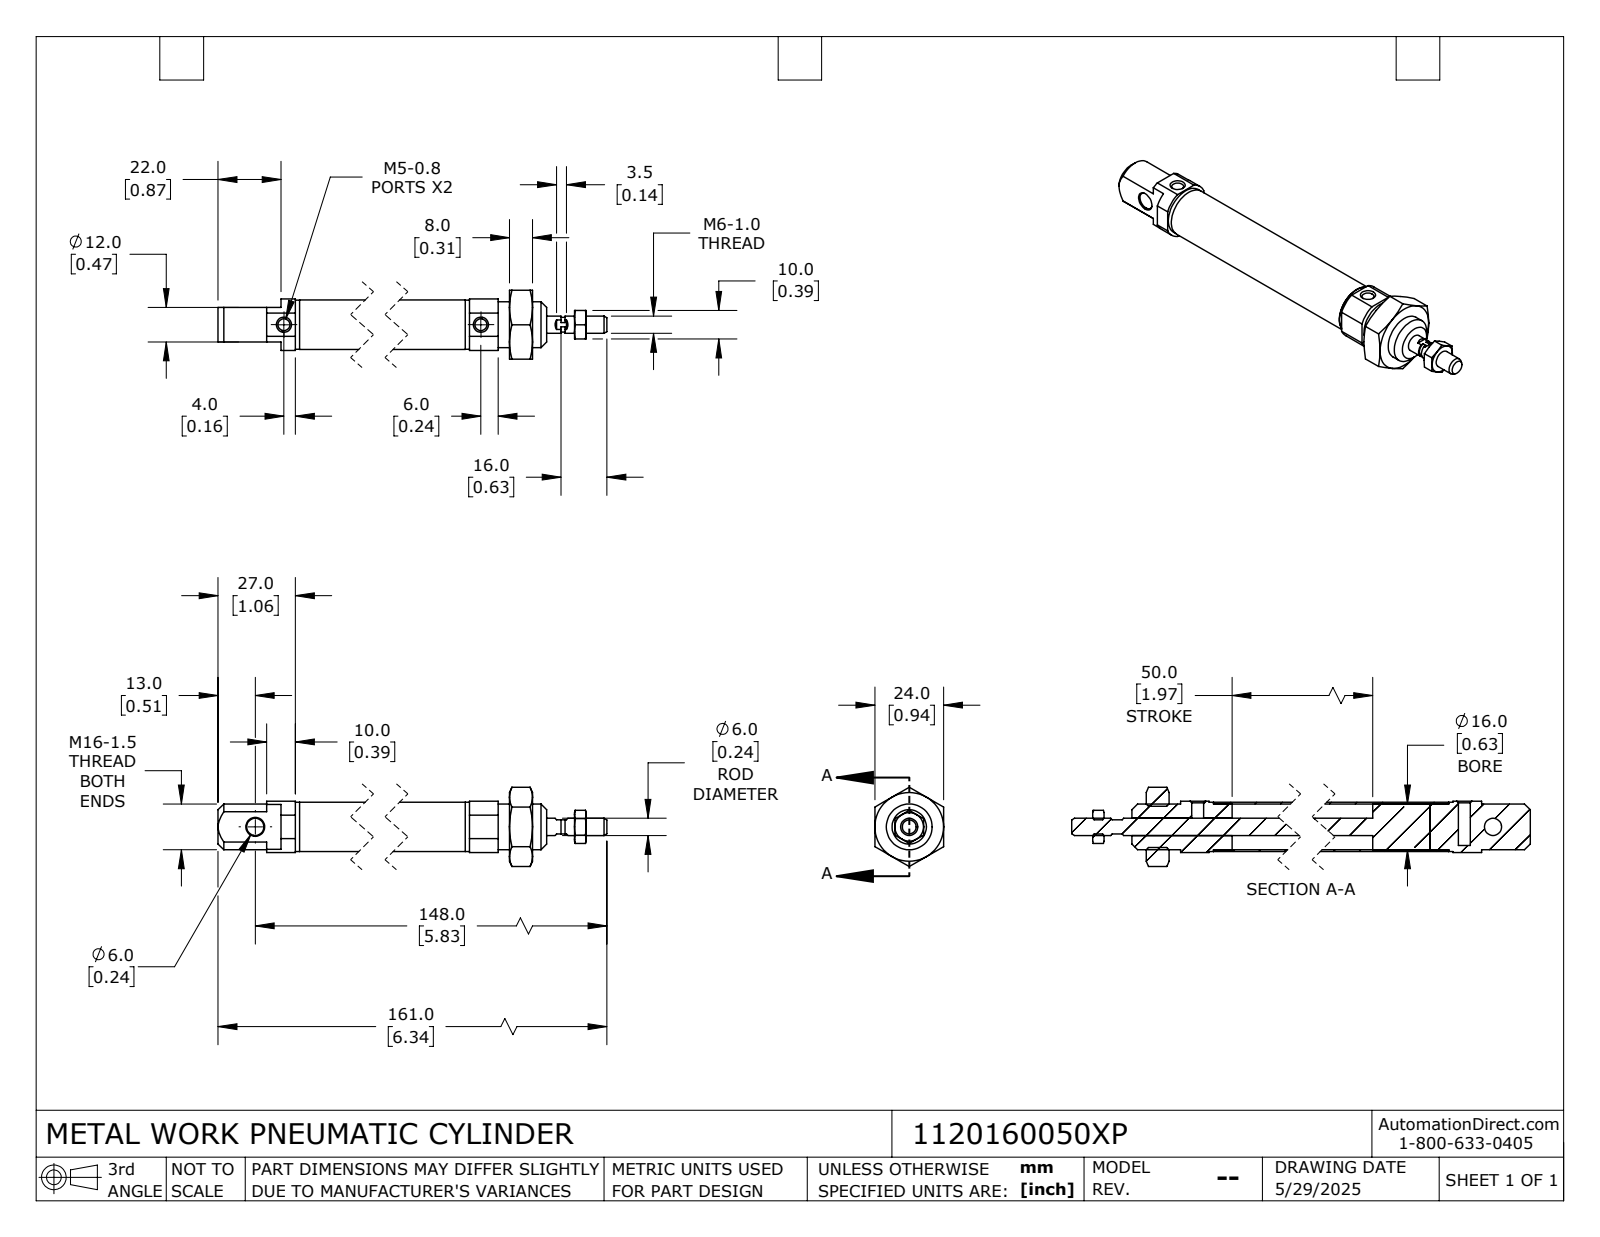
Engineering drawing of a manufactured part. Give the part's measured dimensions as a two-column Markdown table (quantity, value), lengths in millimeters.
| quantity | value |
| --- | --- |
| part name | 1120160050XP_BODY; 1120160050XP_ROD; 1120160050XP |
| STEP written by | SolidWorks 2024 (CONFIG_CONTROL_DESIGN) |
| units | millimeters |
| bodies | 6 solids, 146 faces (55 planar, 45 cylindrical, 46 other) |
| overall size | 161 × 27.71 × 24 |
| volume | 25 924 mm³ |
| surface area | 19 830 mm² |
| round holes (diameter × count) | 4.13 × 2, 4.92 × 1, 6 × 1, 14.38 × 1 |
| round bosses / shafts (diameter × count) | 17.27 × 1, 17.2 × 1, 16.15 × 1, 16 × 1, 6 × 1, 5.2 × 1 |
| partial cylindrical surfaces (radius × count) | 9.85 × 1 |
| main face-to-face distances | 8, 18, 24, 22, 100, 12, 105, 17, 92, 2.97 |
| hole center spacings | 94 |
